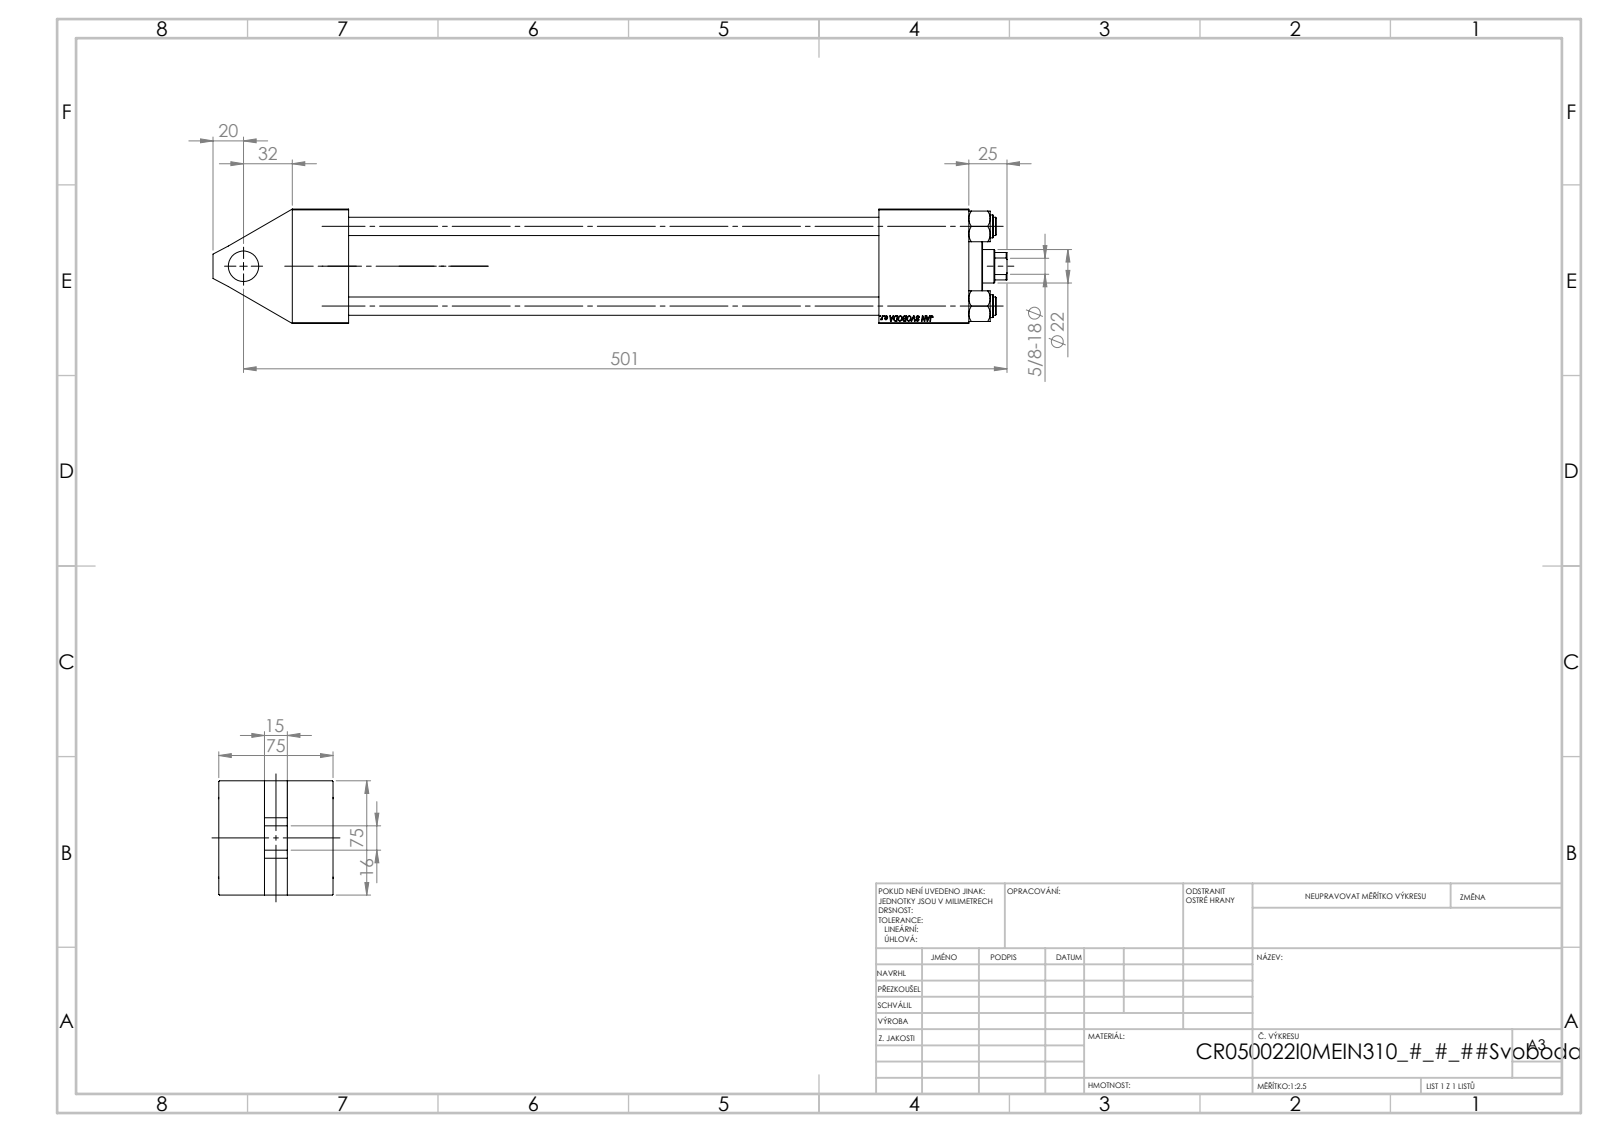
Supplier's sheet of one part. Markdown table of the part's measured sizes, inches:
| quantity | value |
| --- | --- |
| part name | V215CR_I_Body; V215CR_VCP_I; NUT_M5_I; V215_VC_A (+1 more) |
| STEP written by | SolidWorks 2019 (CONFIG_CONTROL_DESIGN) |
| units | inches |
| bodies | 11 solids, 1078 faces (502 planar, 80 cylindrical, 496 other) |
| overall size | 20.512 × 2.974 × 2.953 |
| volume | 66.27 in³ |
| surface area | 490.6 in² |
| round holes (diameter × count) | 0.472 × 4, 0.276 × 2, 0.825 × 2, 1.181 × 2, 0.413 × 1, 0.787 × 1, 0.866 × 1, 0.984 × 1, 1.614 × 1, 1.969 × 1, 2.087 × 1 |
| round bosses / shafts (diameter × count) | 0.591 × 4, 2.205 × 1, 1.339 × 1 |
| partial cylindrical surfaces (radius × count) | 0.413 × 1 |
| main face-to-face distances | 2.953, 16.024, 1.457, 17.48, 1.772, 1.181, 15.157, 13.701, 2.323, 16.35 |
| hole center spacings | 1.456, 2.059, 2.912, 15.098 |
